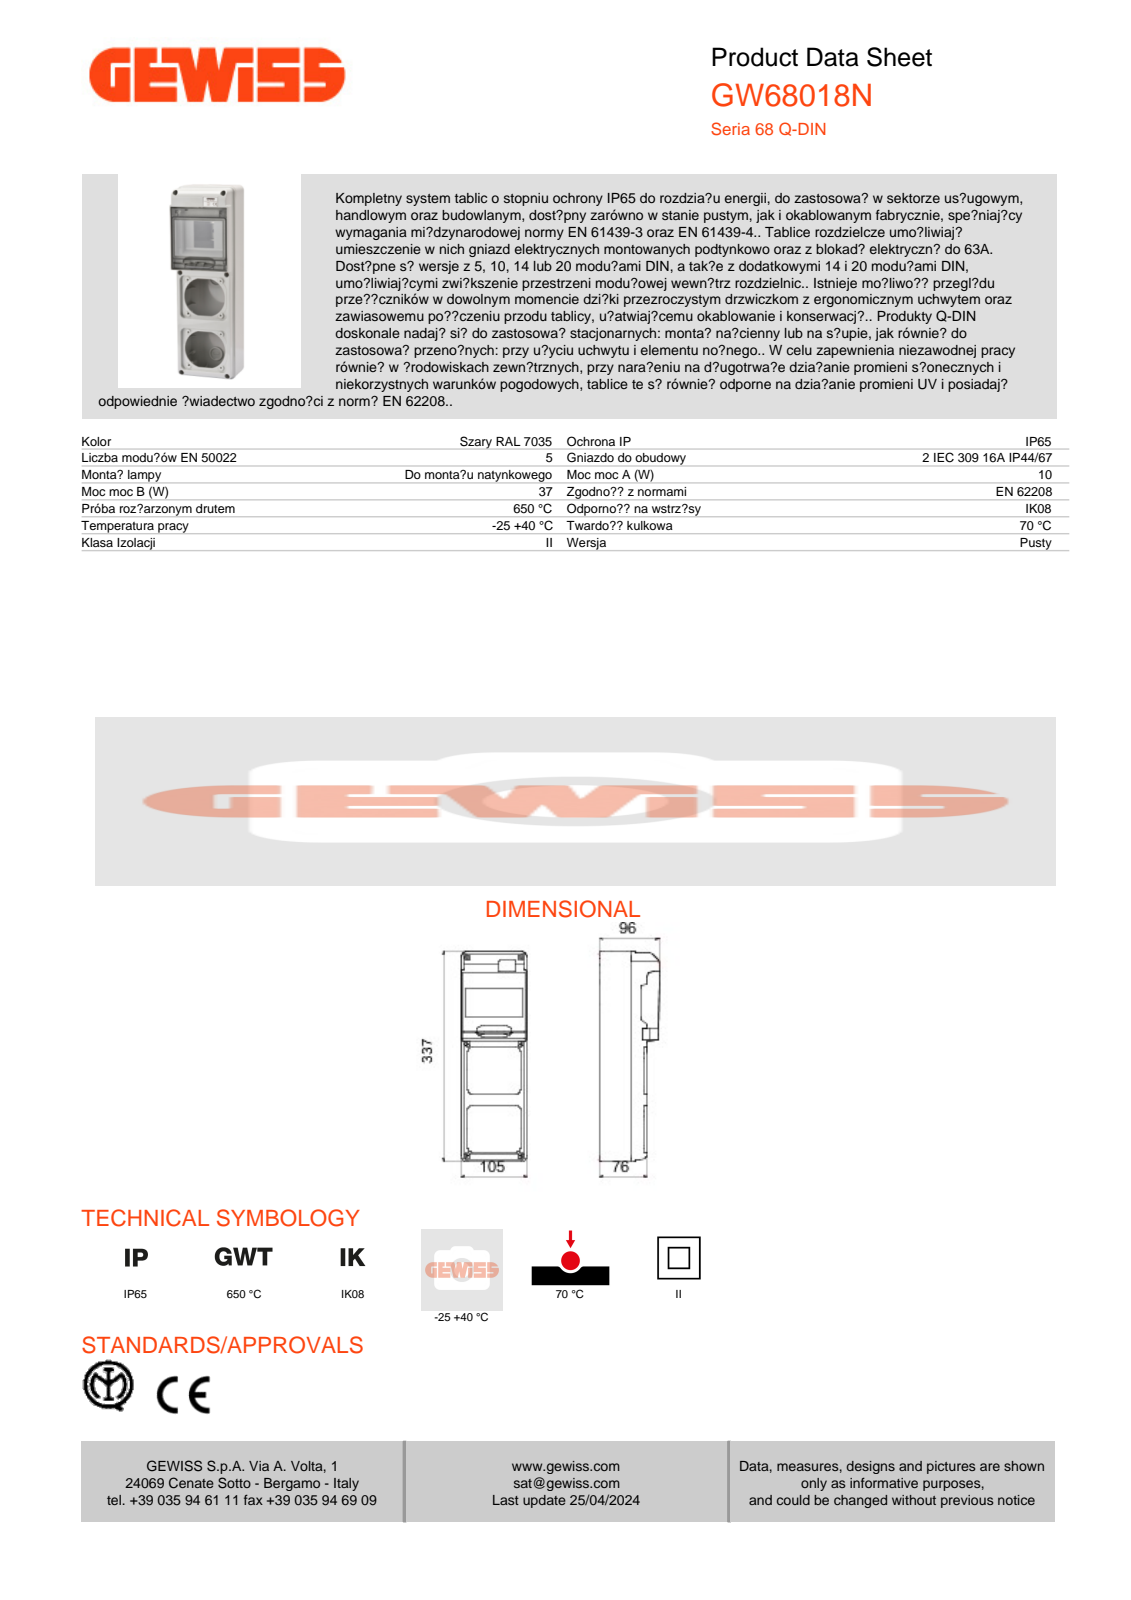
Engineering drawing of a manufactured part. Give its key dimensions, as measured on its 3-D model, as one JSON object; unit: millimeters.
{"part_name": "55524193A_FONDO_QDIN_4M_2_PR_16; 55524201E_NEW; GW68018N_ASM", "step_written_by": "CREO PARAMETRIC BY PTC INC, 2020354 (CONFIG_CONTROL_DESIGN)", "units": "millimeters", "bodies": {"solids": 2, "faces": 589, "planar": 353, "cylindrical": 63, "other": 173}, "overall_size": [337, 105, 100.06], "volume_mm3": 646791, "surface_area_mm2": 292807, "partial_cylinders_radius": [[1.5, 8], [2.5, 8], [0.5, 7], [1, 7], [10, 6], [2, 5], [3, 4], [33.5, 4]], "face_to_face_distances": [2.5, 105, 2.24, 97.09, 94, 91.5, 99.33, 20.5, 73.5, 71]}
